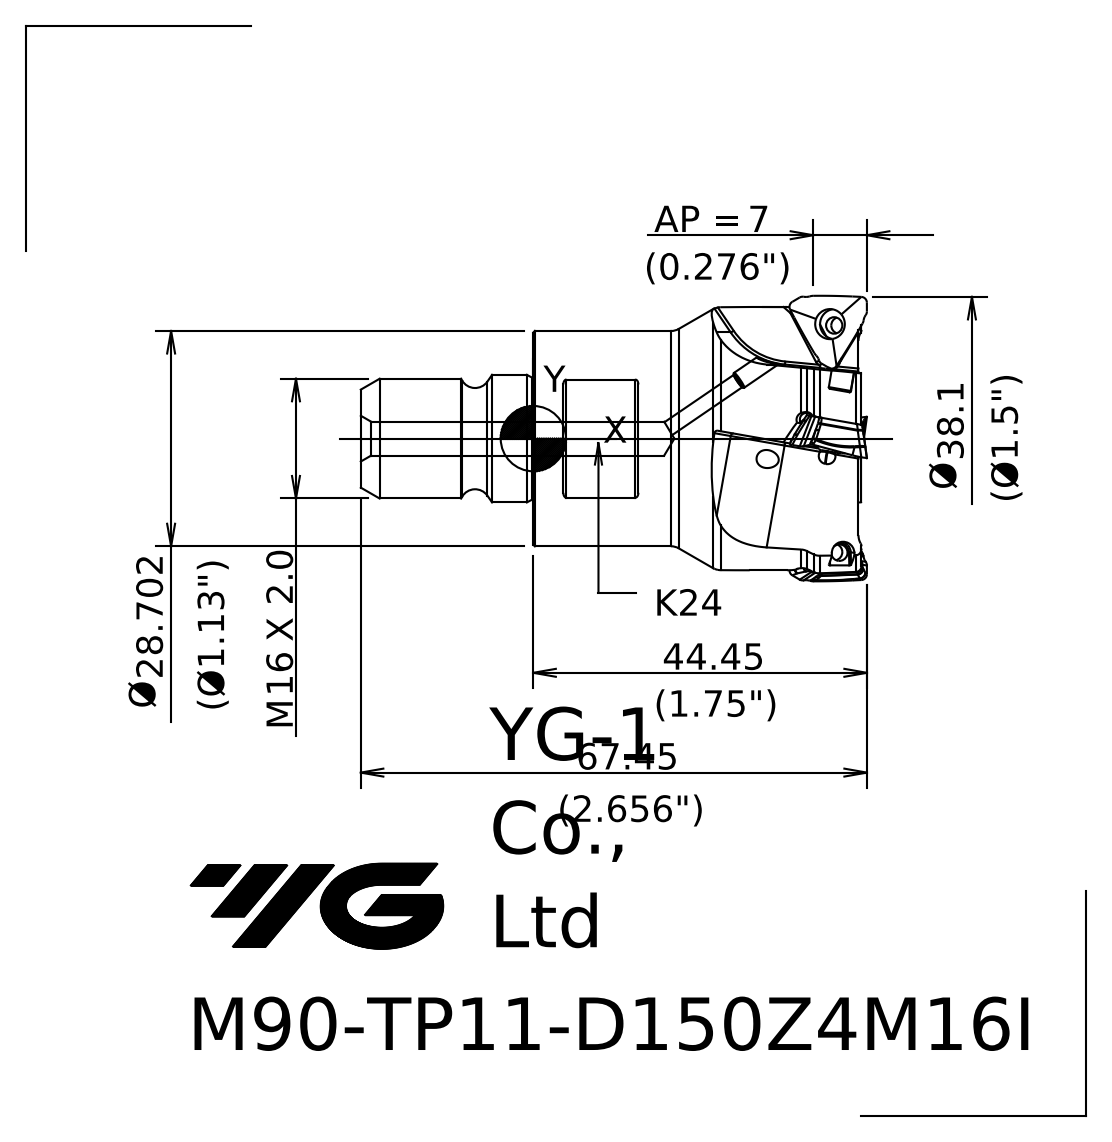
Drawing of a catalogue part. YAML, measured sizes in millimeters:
part_name: "1022B47C5B4Epcah"
step_written_by: "SIEMENS PLM Software NX 10.0 (AP203_CONFIGURATION_CONTROLLED_3D_DESIGN_OF_MECHANICAL_PARTS_AND_ASSEMBLIES_MIM_LF)"
units: millimeters
bodies: {solids: 1, faces: 66, planar: 10, cylindrical: 10, other: 46}
overall_size: [67.45, 38.13, 38.13]
volume: 38670
surface_area: 10982
round_holes:
  - {diameter: 1.5, count: 1}
  - {diameter: 4.5, count: 1}
round_bosses_or_shafts:
  - {diameter: 35.1, count: 1}
  - {diameter: 28.7, count: 1}
  - {diameter: 17, count: 1}
  - {diameter: 15.96, count: 1}
partial_cylinders:
  - {radius: 0.4, count: 4}
face_to_face_distances: [43.35, 24, 66.35, 23, 29.35, 14, 37, 39.35, 10, 4]
